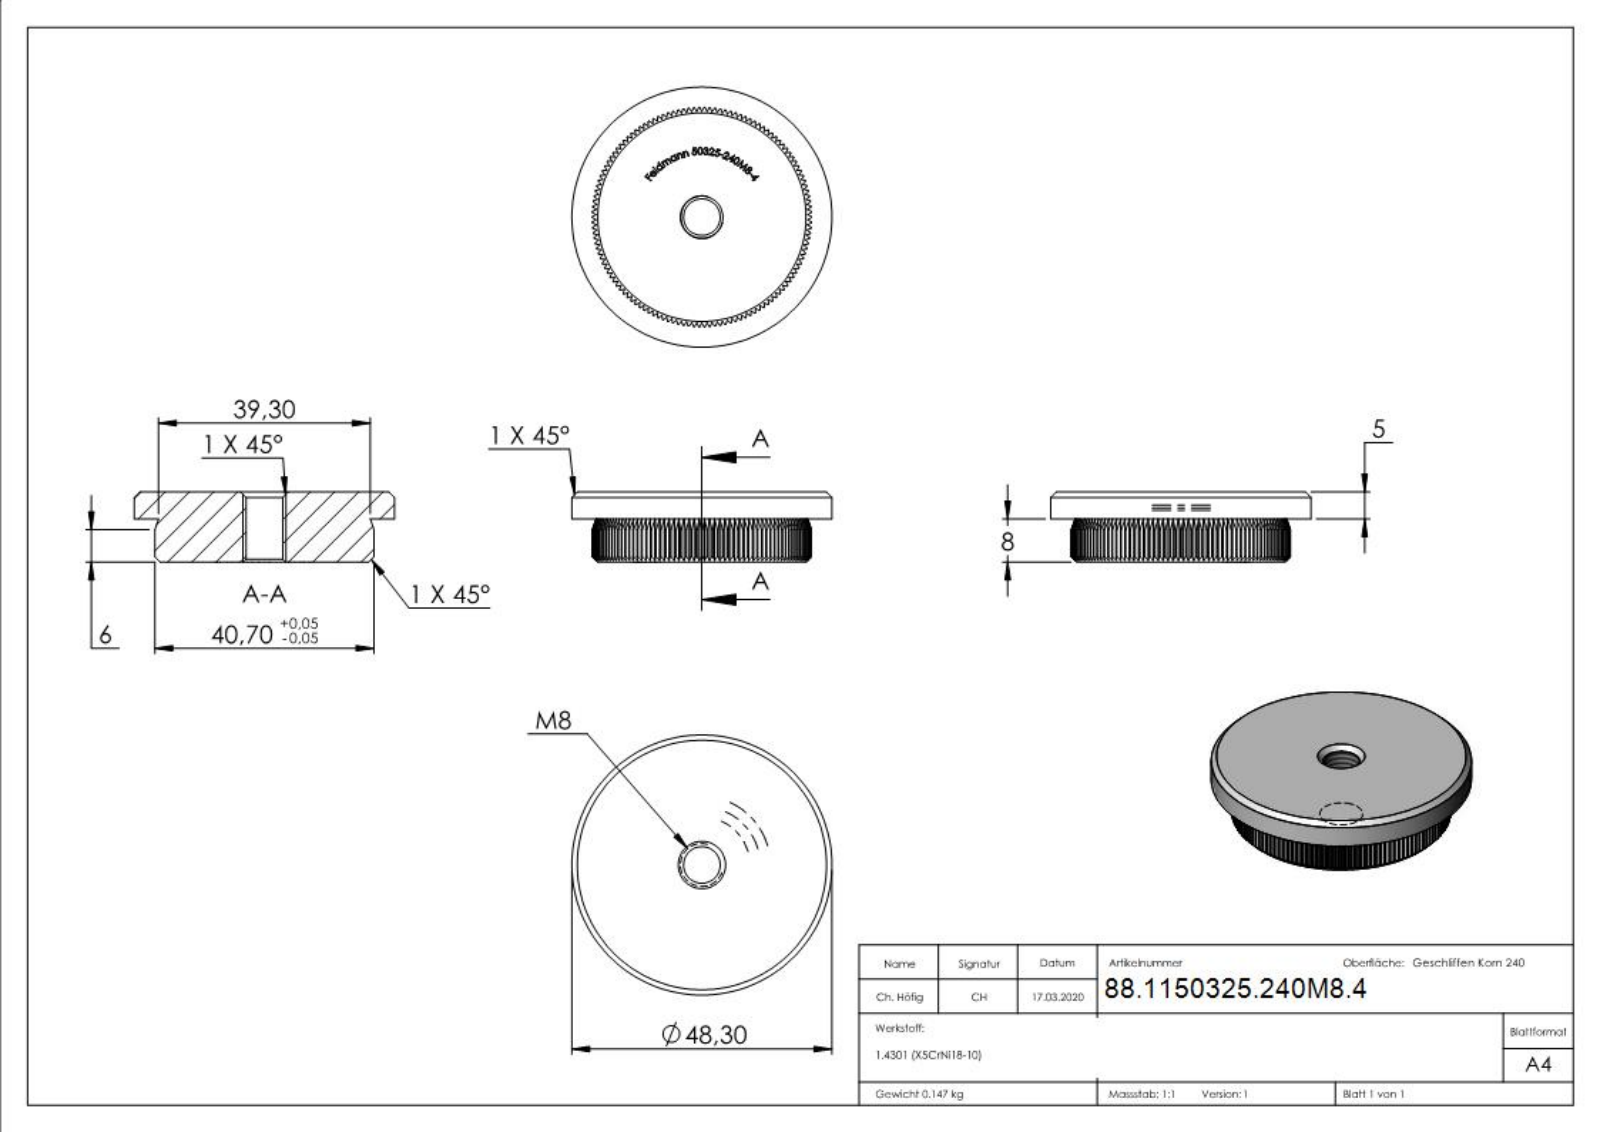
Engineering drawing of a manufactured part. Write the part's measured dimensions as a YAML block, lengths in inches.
part_name: "50325-240M8-4"
step_written_by: "SolidWorks 2015 (CONFIG_CONTROL_DESIGN)"
units: inches
bodies: {solids: 1, faces: 812, planar: 421, cylindrical: 132, other: 259}
overall_size: [1.902, 1.902, 0.512]
volume: 1.137
surface_area: 9.643
round_holes:
  - {diameter: 0.268, count: 1}
round_bosses_or_shafts:
  - {diameter: 1.902, count: 1}
partial_cylinders:
  - {radius: 0.801, count: 1}
face_to_face_distances: [0.512, 0.315, 0.197, 0.773, 0.774, 0.775, 0.772, 0.311, 0.508, 0.376]
